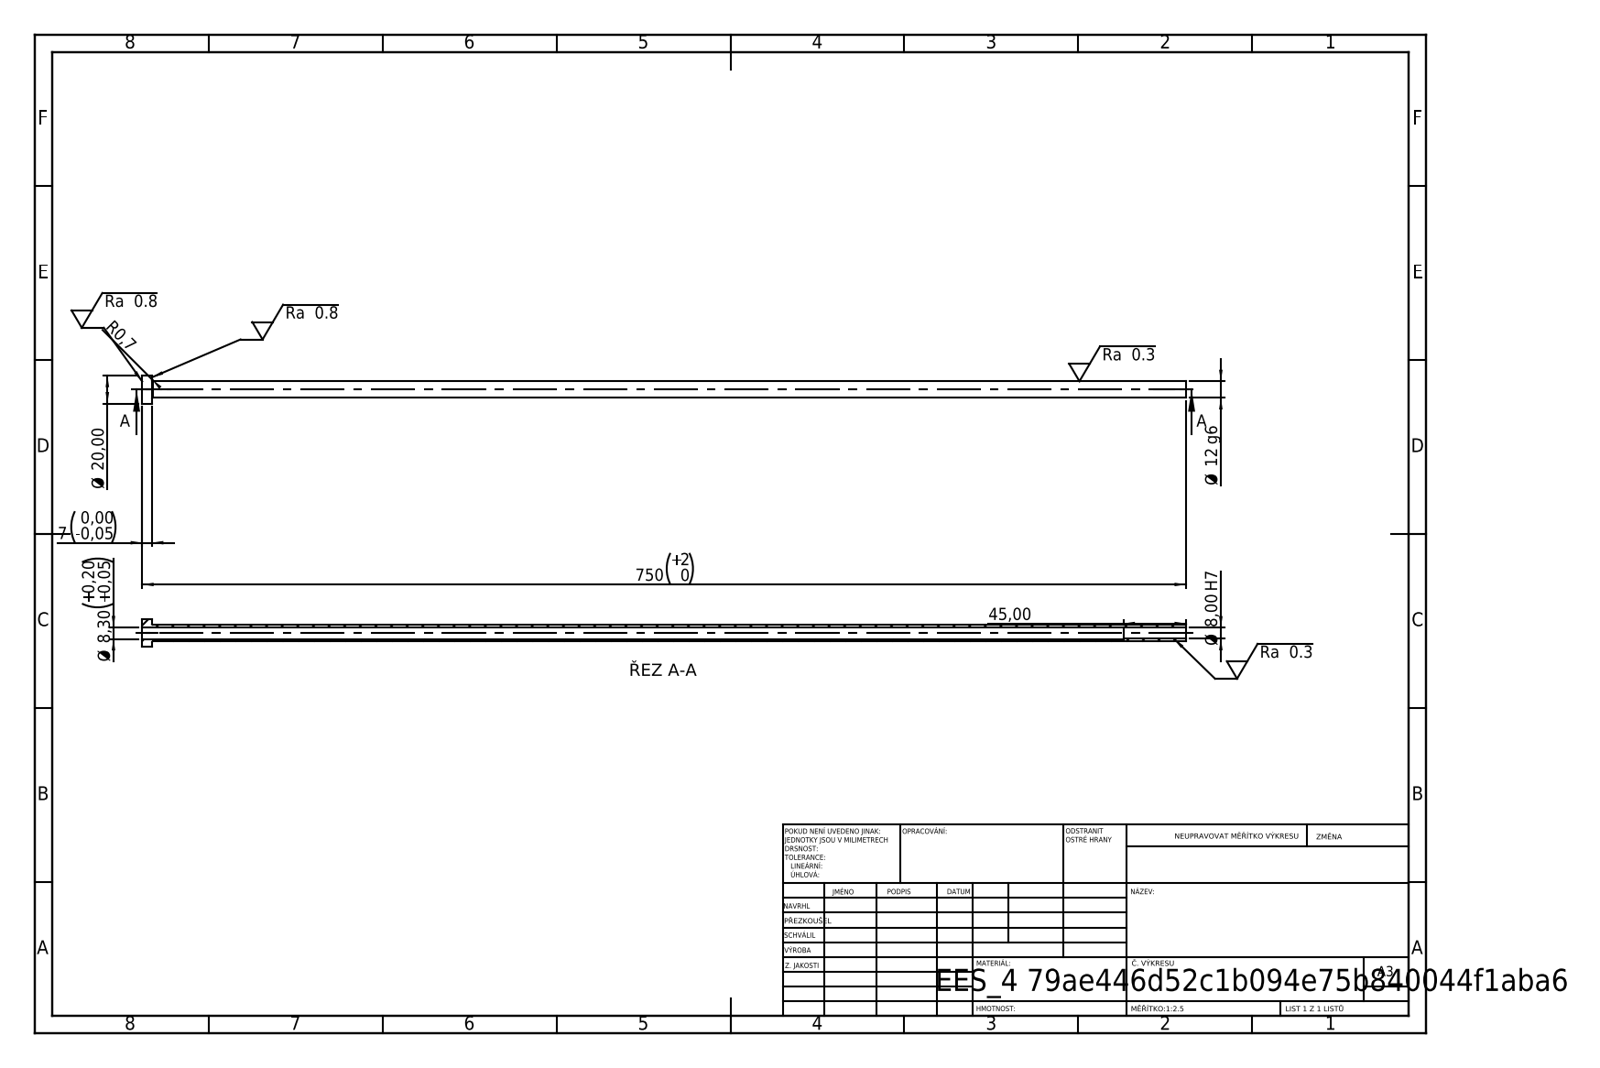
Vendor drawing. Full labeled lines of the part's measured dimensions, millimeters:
STEP written by: SolidWorks 2019 (CONFIG_CONTROL_DESIGN)
Units: millimetres
Bodies: 1 solid, 14 faces (4 planar, 8 cylindrical, 2 other)
Overall size (bounding box): 750 × 20 × 20
Volume: 45 828 mm³ · Surface area: 48 481 mm²
Round holes (diameter × count): ⌀8 ×1, ⌀8.3 ×1
Round bosses / shafts (diameter × count): ⌀20 ×1, ⌀12 ×1
Main face-to-face distances: 7, 750, 743, 705, 698, 45
